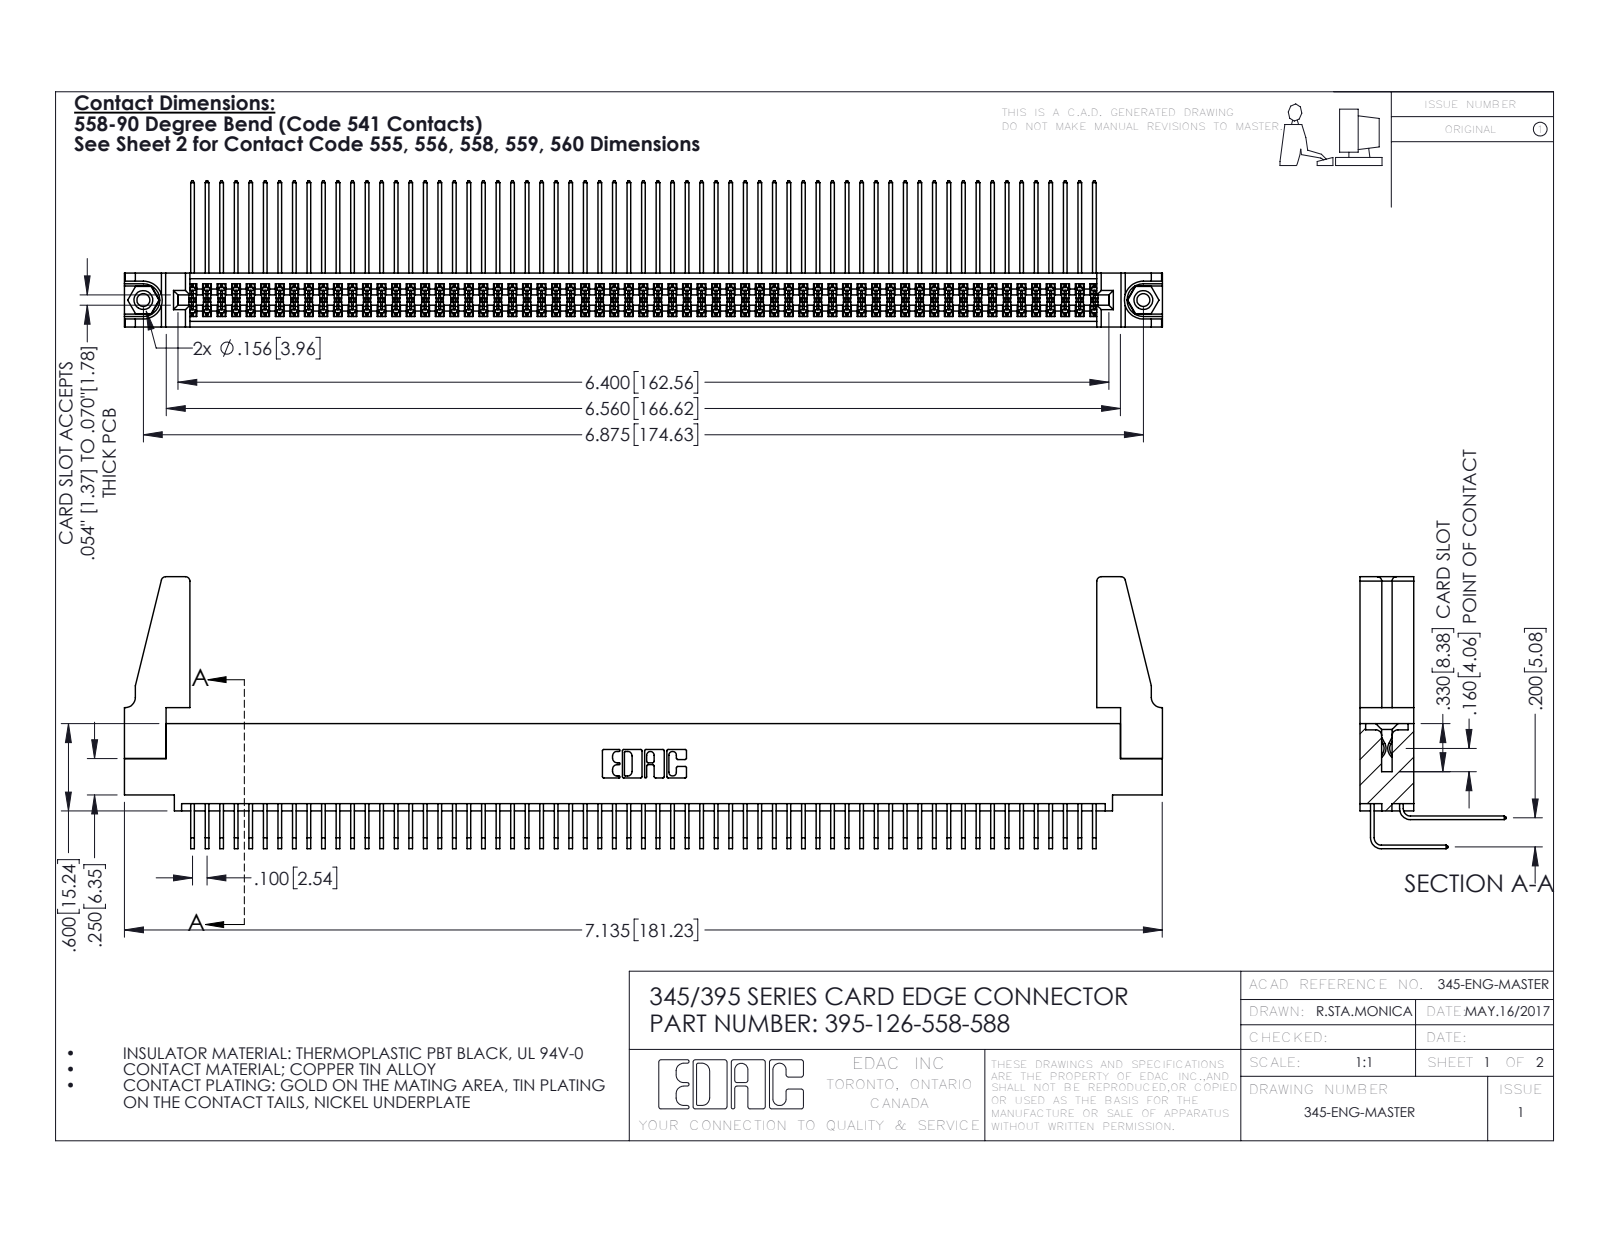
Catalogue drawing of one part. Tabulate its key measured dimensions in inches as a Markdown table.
| quantity | value |
| --- | --- |
| part name | 345-220-078_345-220-088; 345-292-001_558 Tail - 2; 345-292-001_558 559 Tail - 1; 345 Part_0.110 Offset - 0.156 Dia-TH (+2 more) |
| STEP written by | SolidWorks 2016 (CONFIG_CONTROL_DESIGN) |
| units | inches |
| bodies | 131 solids, 6806 faces (4566 planar, 2224 cylindrical, 16 other) |
| overall size | 7.136 × 1.869 × 1.005 |
| volume | 1.325 in³ |
| surface area | 53.2 in² |
| round holes (diameter × count) | 0.089 × 2, 0.125 × 2, 0.156 × 2, 0.064 × 1 |
| round bosses / shafts (diameter × count) | 0.155 × 2 |
| partial cylindrical surfaces (radius × count) | 0.006 × 190, 0.01 × 22, 0.03 × 8, 0.007 × 6, 0.031 × 6, 0.026 × 3, 0.014 × 2, 0.019 × 2 |
| main face-to-face distances | 0.072, 0.298, 0.2, 0.37, 0.098, 0.272, 0.025, 0.225, 0.025, 0.175 |
| hole center spacings | 0.27, 6.639, 6.875 |
